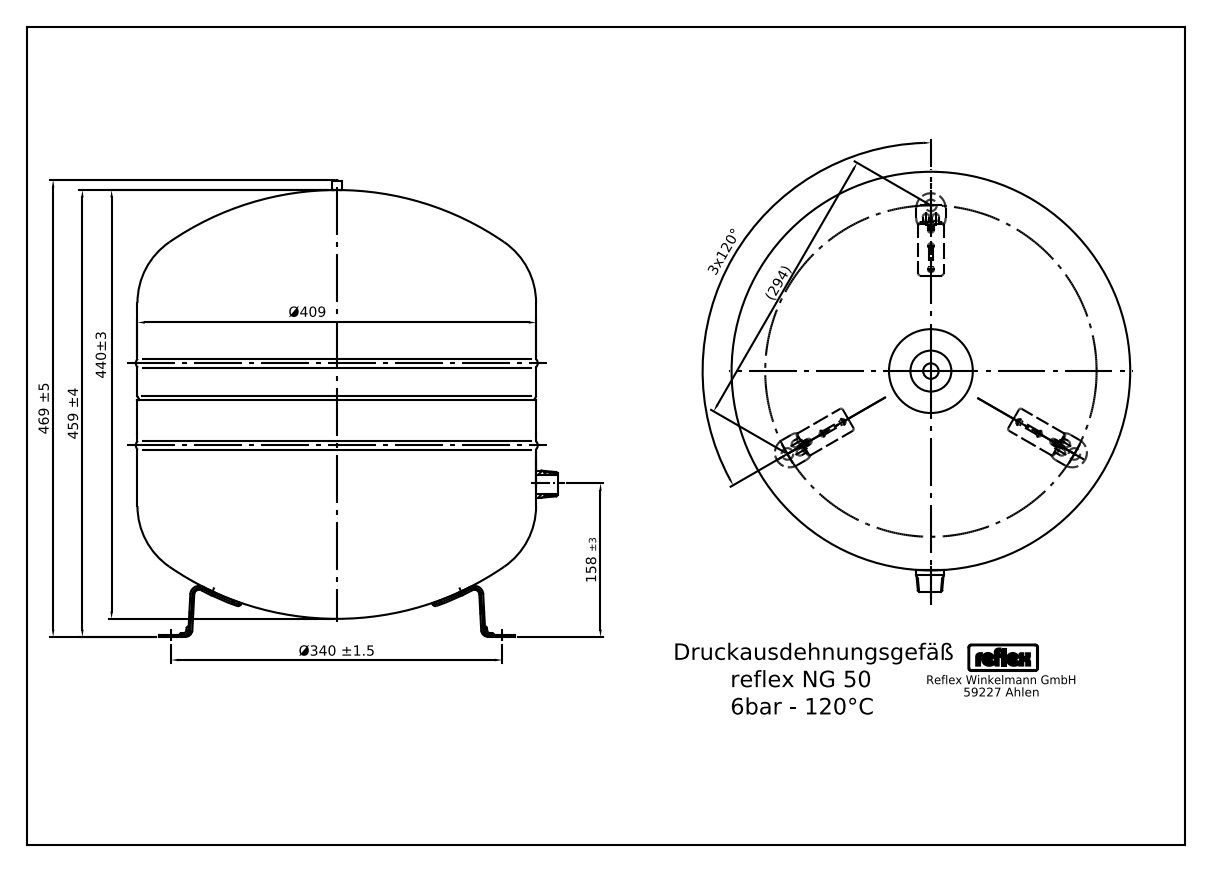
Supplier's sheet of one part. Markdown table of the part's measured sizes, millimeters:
| quantity | value |
| --- | --- |
| STEP written by | Mechanical Desktop 2011 (CONFIG_CONTROL_DESIGN) |
| units | millimeters |
| bodies | 16 solids, 191 faces (76 planar, 74 cylindrical, 41 other) |
| overall size | 495 × 450 × 441 |
| volume | 50 980 000 mm³ |
| surface area | 1 330 000 mm² |
| round holes (diameter × count) | 15 × 3, 20.5 × 1 |
| round bosses / shafts (diameter × count) | 441 × 1, 409 × 1, 26.9 × 1, 10 × 1, 6 × 1 |
| partial cylindrical surfaces (radius × count) | 148.38 × 9, 150.38 × 9, 15 × 6, 2.81 × 4, 1.12 × 3, 1.92 × 2, 3.38 × 2, 4.64 × 2 |
| main face-to-face distances | 241, 109.75, 131.25, 21.5, 240.75, 131, 262.25, 372, 2, 129 |
| hole center spacings | 294.45, 294.44 |
